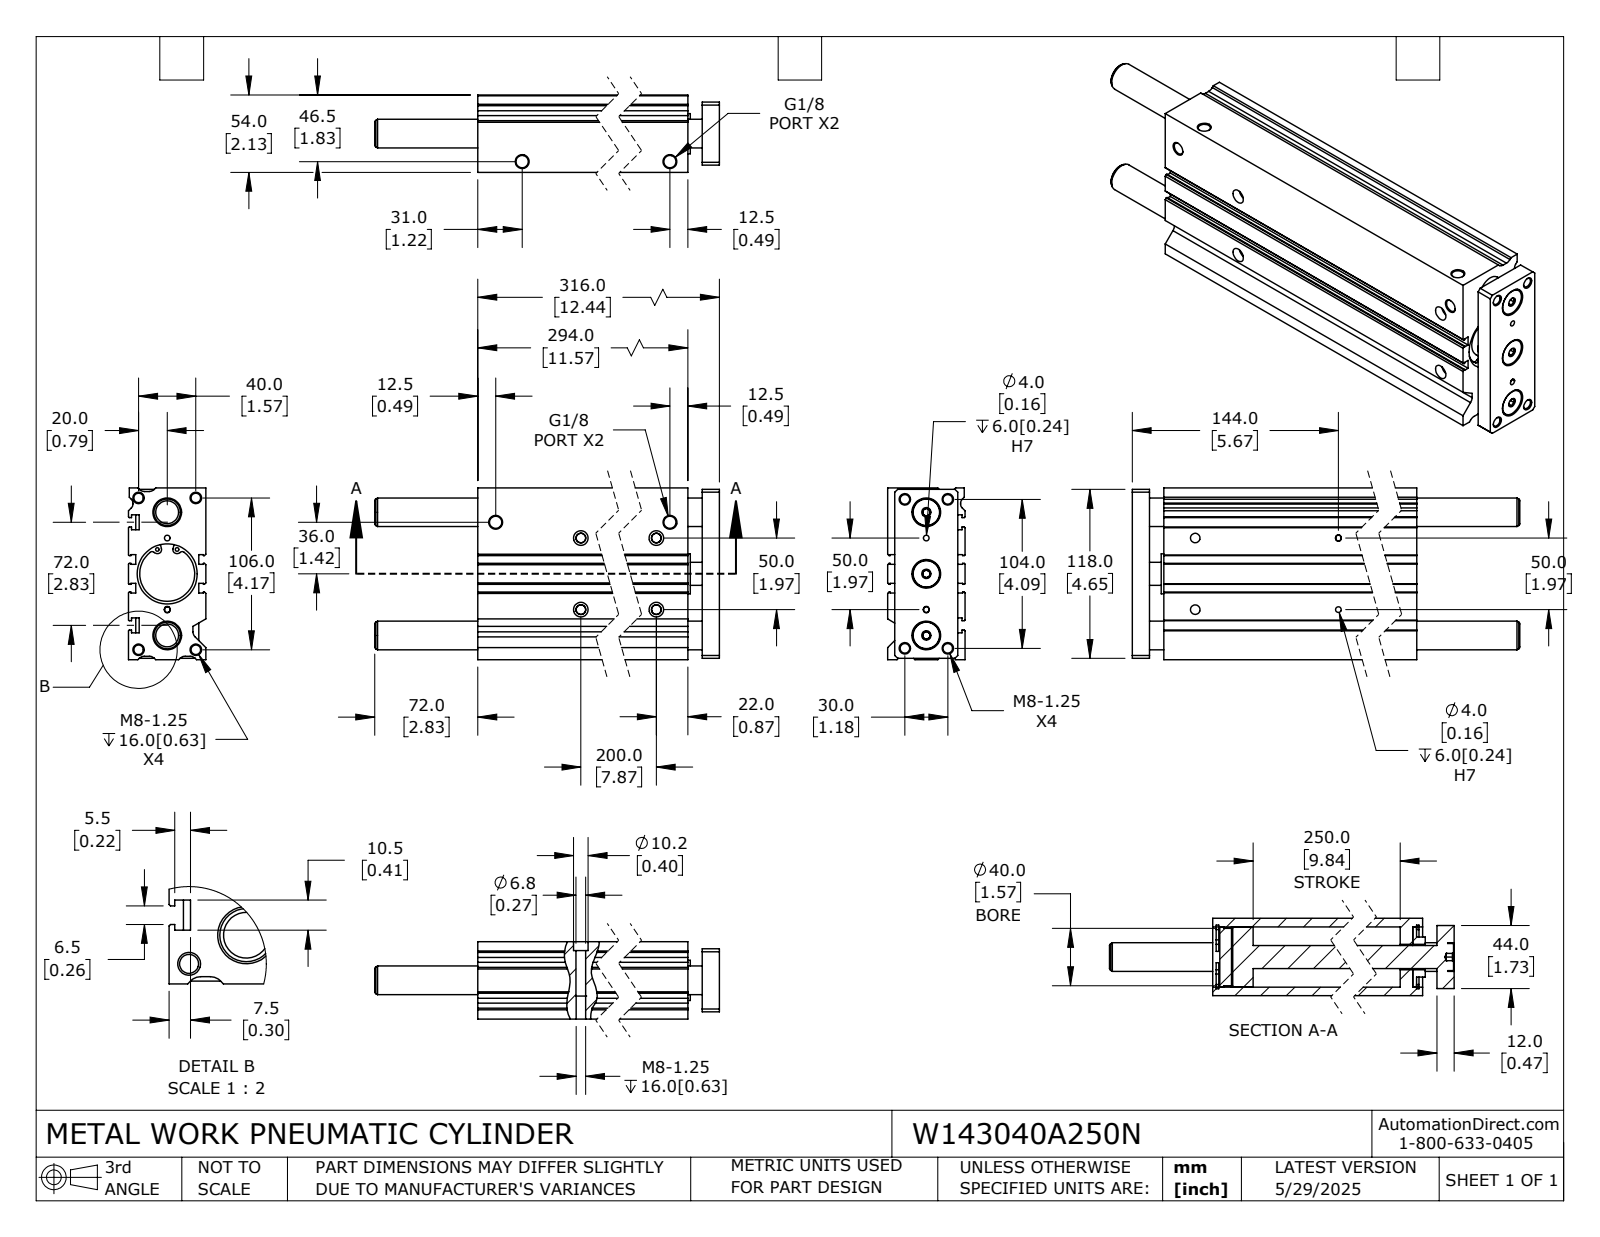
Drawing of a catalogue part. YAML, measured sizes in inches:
part_name: "W143040A250N_BODY; W143040A250N; W143040A250N_ROD"
step_written_by: "SolidWorks 2024 (CONFIG_CONTROL_DESIGN)"
units: inches
bodies: {solids: 6, faces: 393, planar: 192, cylindrical: 151, other: 50}
overall_size: [15.276, 4.724, 2.126]
volume: 95.09
surface_area: 493.9
round_holes:
  - {diameter: 0.262, count: 12}
  - {diameter: 0.098, count: 4}
  - {diameter: 0.157, count: 4}
  - {diameter: 0.268, count: 4}
  - {diameter: 0.337, count: 4}
  - {diameter: 0.402, count: 4}
  - {diameter: 0.197, count: 3}
  - {diameter: 0.787, count: 3}
  - {diameter: 0.697, count: 1}
  - {diameter: 1.51, count: 1}
round_bosses_or_shafts:
  - {diameter: 0.748, count: 3}
  - {diameter: 1.752, count: 2}
  - {diameter: 1.654, count: 1}
  - {diameter: 1.575, count: 1}
  - {diameter: 1.102, count: 1}
  - {diameter: 0.63, count: 1}
partial_cylinders:
  - {radius: 0.197, count: 7}
  - {radius: 0.079, count: 4}
  - {radius: 0.089, count: 4}
  - {radius: 0.116, count: 4}
  - {radius: 0.157, count: 2}
face_to_face_distances: [2.126, 0.197, 1.929, 0.098, 4.724, 0.295, 1.831, 1.634, 1.732, 0.276]
hole_center_spacings: [0.201, 0.415, 0.689, 0.722, 0.88, 1.059, 1.216, 1.355]
